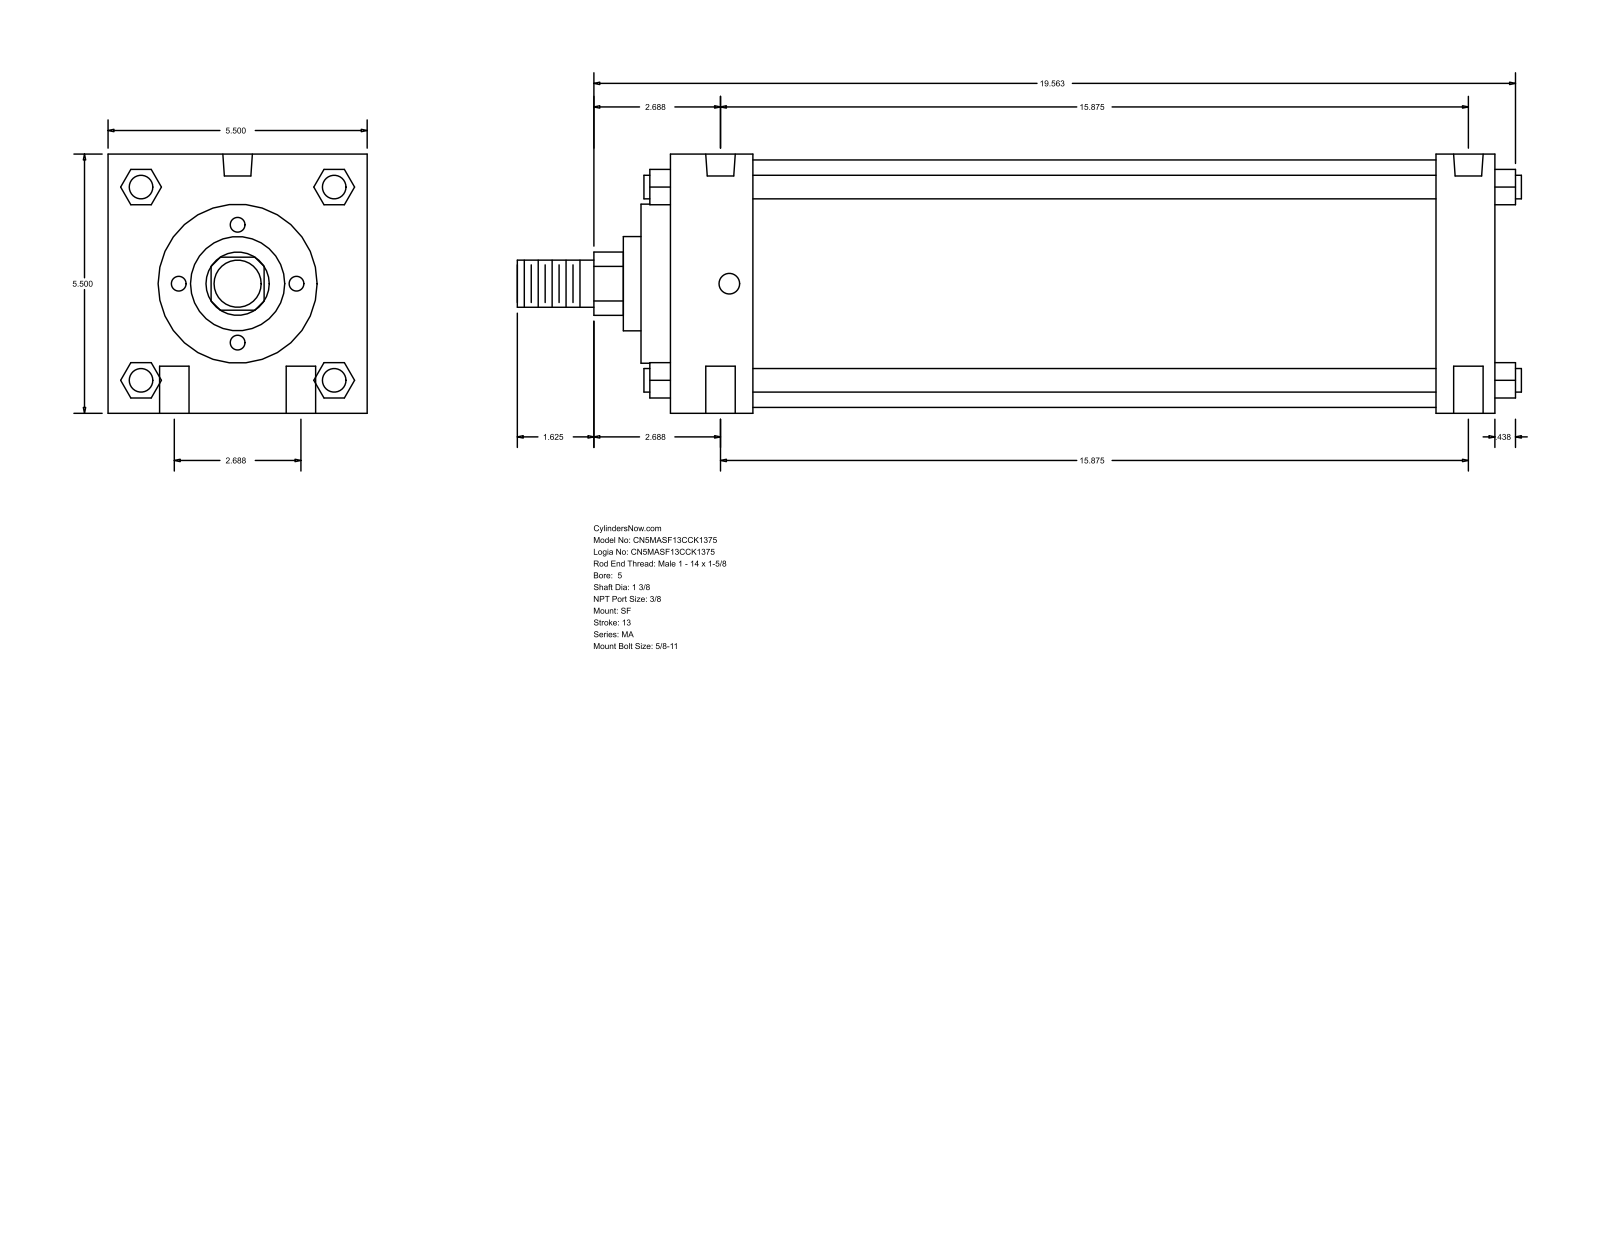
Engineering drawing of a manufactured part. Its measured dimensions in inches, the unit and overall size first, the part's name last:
Units: inches
Overall size (bounding box): 21.313 × 5.5 × 5.5
Round holes (diameter × count): ⌀0.625 ×4, ⌀0.437 ×2, ⌀0.627 ×2
Round bosses / shafts (diameter × count): ⌀0.5 ×4, ⌀5.25 ×1, ⌀3.375 ×1, ⌀2 ×1, ⌀1.375 ×1, ⌀1 ×1
Partial cylindrical surfaces — rounded edges, fillets, slot ends (radius × count): R0.672 ×1
Main face-to-face distances: 5.5, 17.5, 1.75, 16.25, 14.5, 15.75, 1.25, 0.625, 2.375, 16.875
Hole centre spacings: 1.344, 15.932, 15.875, 2.687, 16.101, 15.5
Bodies: 0 solids, 126 faces (95 planar, 31 cylindrical, 0 other)
Part name (STEP PRODUCT): MA_SF__0500_1.375
STEP written by: GSSL Pune (CONFIG_CONTROL_DESIGN)
